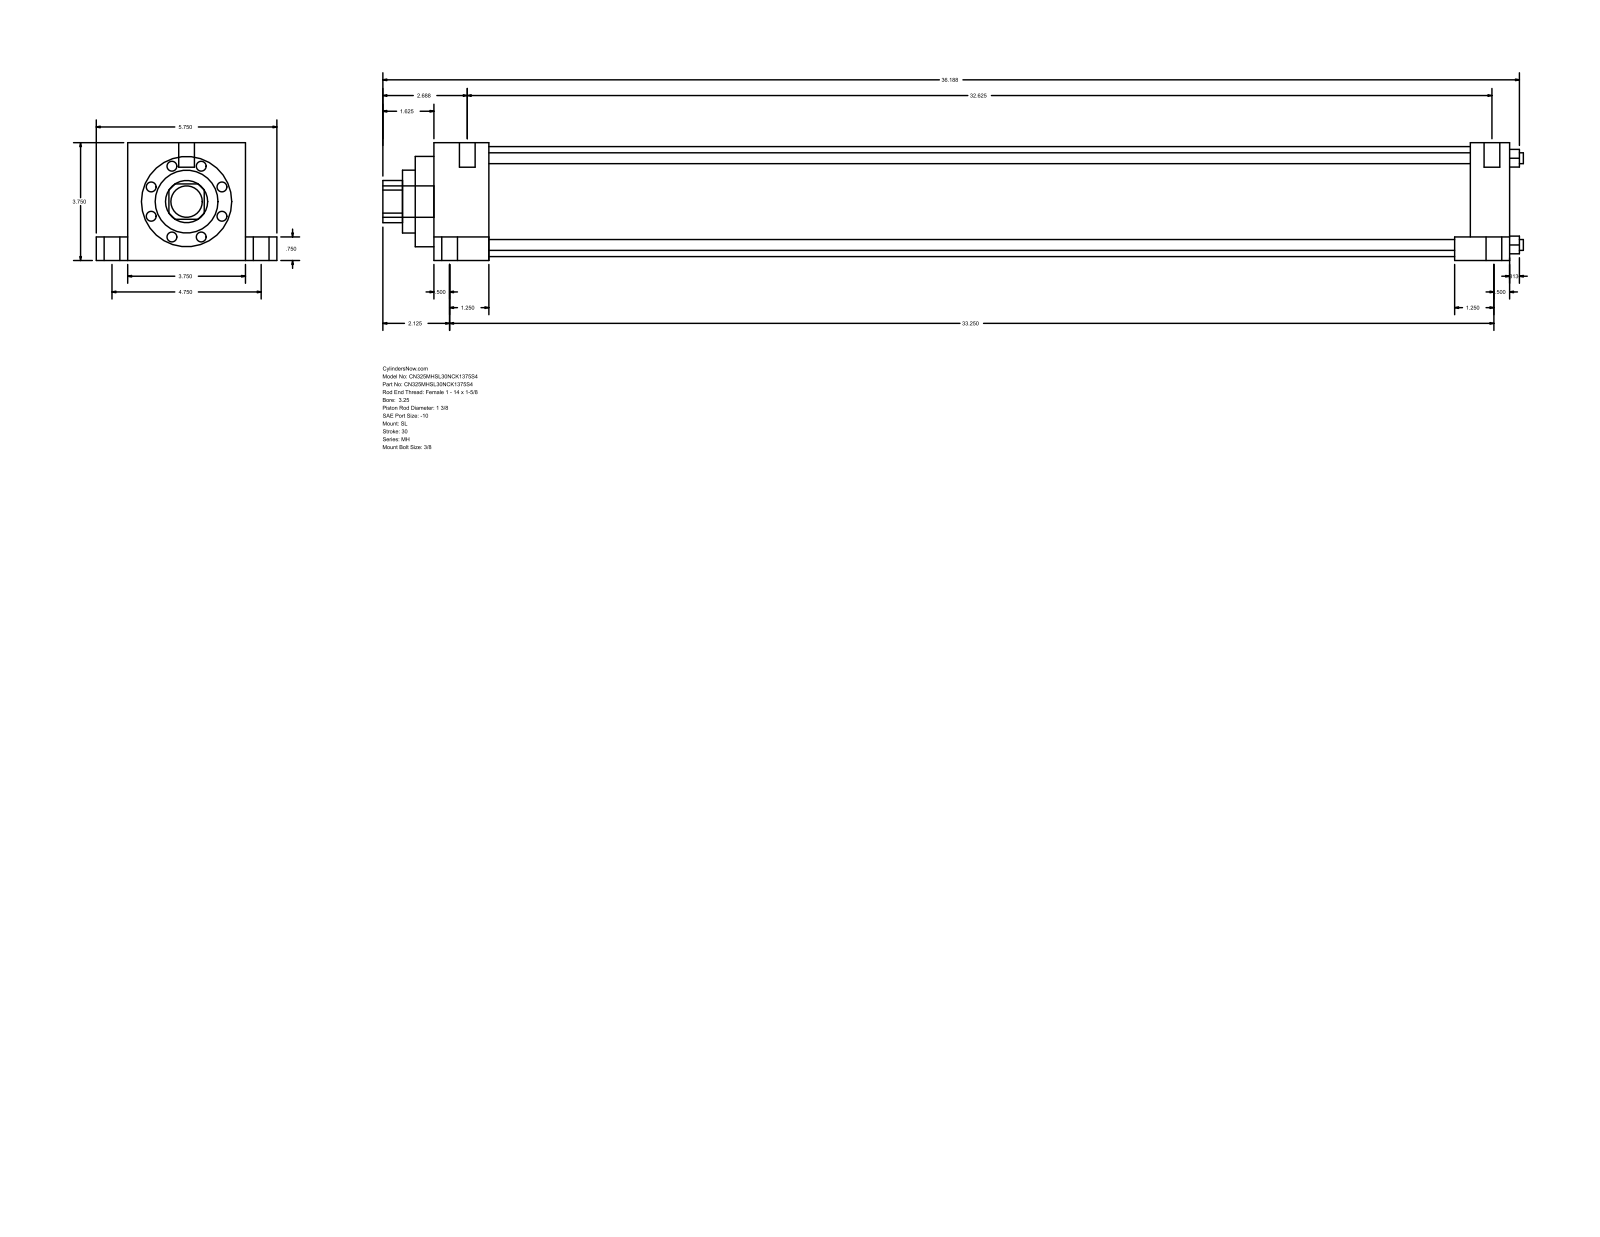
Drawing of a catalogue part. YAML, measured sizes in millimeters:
part_name: "MH_SL__0325_1.375"
step_written_by: "GSSL Pune (CONFIG_CONTROL_DESIGN)"
units: millimeters
bodies: {solids: 0, faces: 110, planar: 77, cylindrical: 33, other: 0}
overall_size: [922.34, 146.05, 95.25]
round_holes:
  - {diameter: 8.76, count: 4}
  - {diameter: 34.92, count: 1}
  - {diameter: 50.8, count: 1}
  - {diameter: 73.03, count: 1}
  - {diameter: 88.9, count: 1}
round_bosses_or_shafts:
  - {diameter: 12.7, count: 6}
  - {diameter: 19.05, count: 4}
  - {diameter: 5.56, count: 4}
  - {diameter: 25.4, count: 1}
partial_cylinders:
  - {radius: 17.06, count: 1}
face_to_face_distances: [95.24, 869.96, 44.45, 825.51, 25.41, 120.65, 19.05, 76.19, 838.21, 793.76]
hole_center_spacings: [49.57, 70.1, 99.14]
